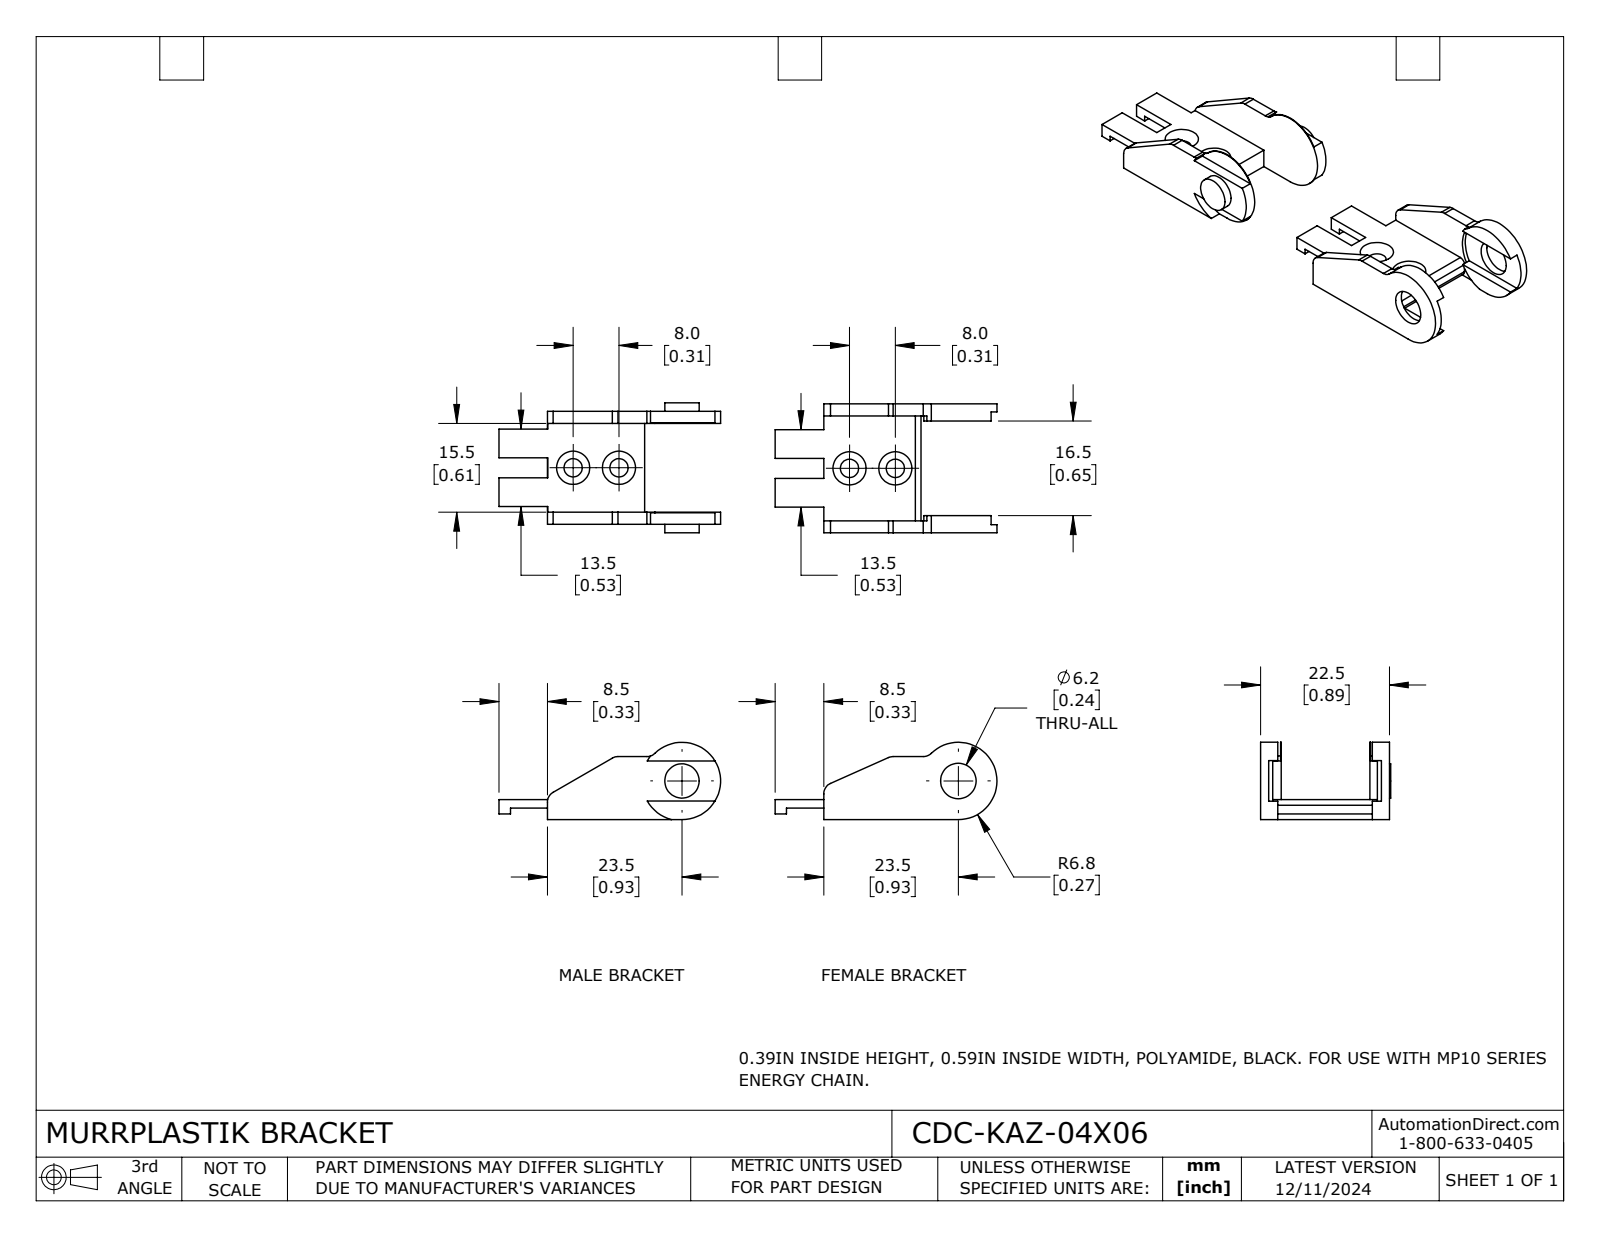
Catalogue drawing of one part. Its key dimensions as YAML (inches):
part_name: "CDC-KAZ-04X06"
step_written_by: "SolidWorks 2024 (AUTOMOTIVE_DESIGN)"
units: inches
bodies: {solids: 2, faces: 109, planar: 68, cylindrical: 37, other: 4}
overall_size: [3.424, 0.894, 0.531]
volume: 0.271
surface_area: 7.586
round_holes:
  - {diameter: 0.126, count: 4}
  - {diameter: 0.244, count: 1}
round_bosses_or_shafts:
  - {diameter: 0.236, count: 1}
partial_cylinders:
  - {radius: 0.079, count: 6}
  - {radius: 0.039, count: 2}
  - {radius: 0.266, count: 2}
  - {radius: 0.276, count: 2}
face_to_face_distances: [0.138, 0.083, 0.059, 0.693, 0.752, 0.744, 0.079, 0.051, 0.776, 0.886]
hole_center_spacings: [0.315, 1.9, 1.585, 2.215]
